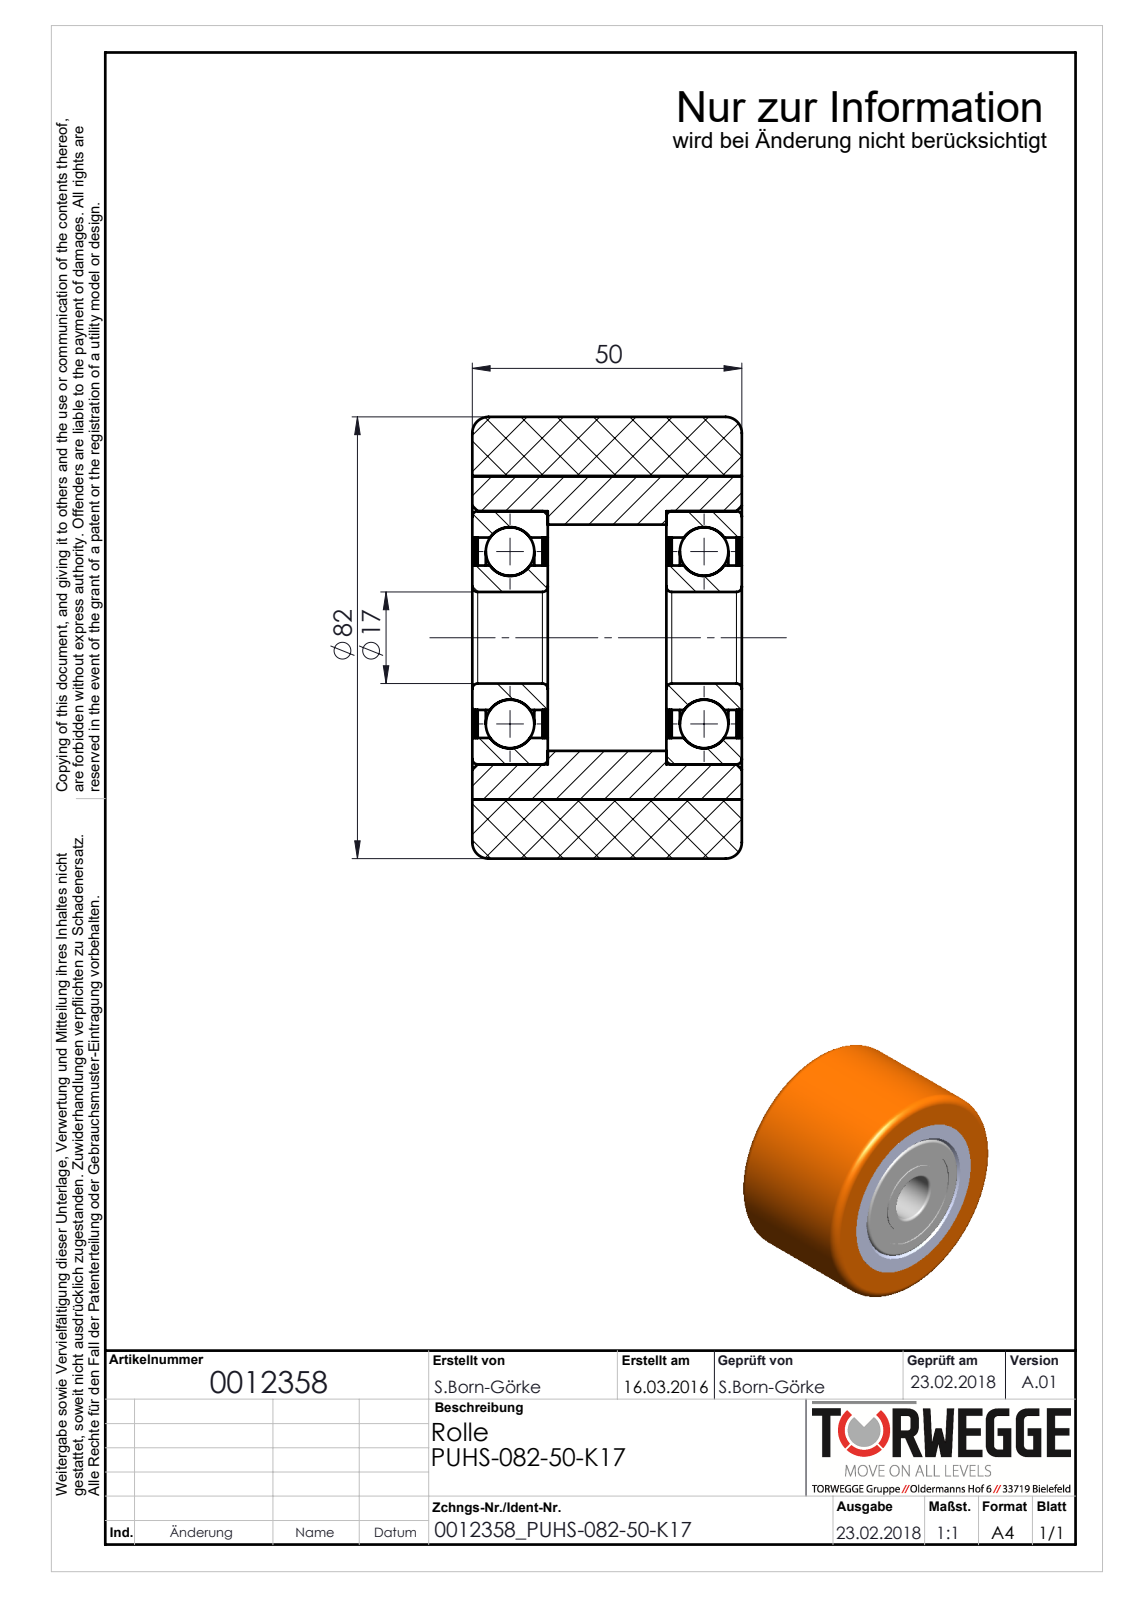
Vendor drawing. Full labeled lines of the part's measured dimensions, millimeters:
Part name (STEP PRODUCT): 0012358_PUHS-082-50-K17
STEP written by: SolidWorks 2016 (AUTOMOTIVE_DESIGN)
Units: millimetres
Bodies: 12 solids, 118 faces (22 planar, 52 cylindrical, 44 other)
Overall size (bounding box): 82 × 82 × 50
Volume: 220 827 mm³ · Surface area: 71 378 mm²
Round holes (diameter × count): ⌀17 ×1, ⌀26.8 ×1, ⌀37.2 ×1, ⌀42 ×1, ⌀47 ×1, ⌀60 ×1
Round bosses / shafts (diameter × count): ⌀82 ×1
Main face-to-face distances: 36, 0.5, 50, 13, 14, 1, 13.5, 36.5, 12.5, 35.5
